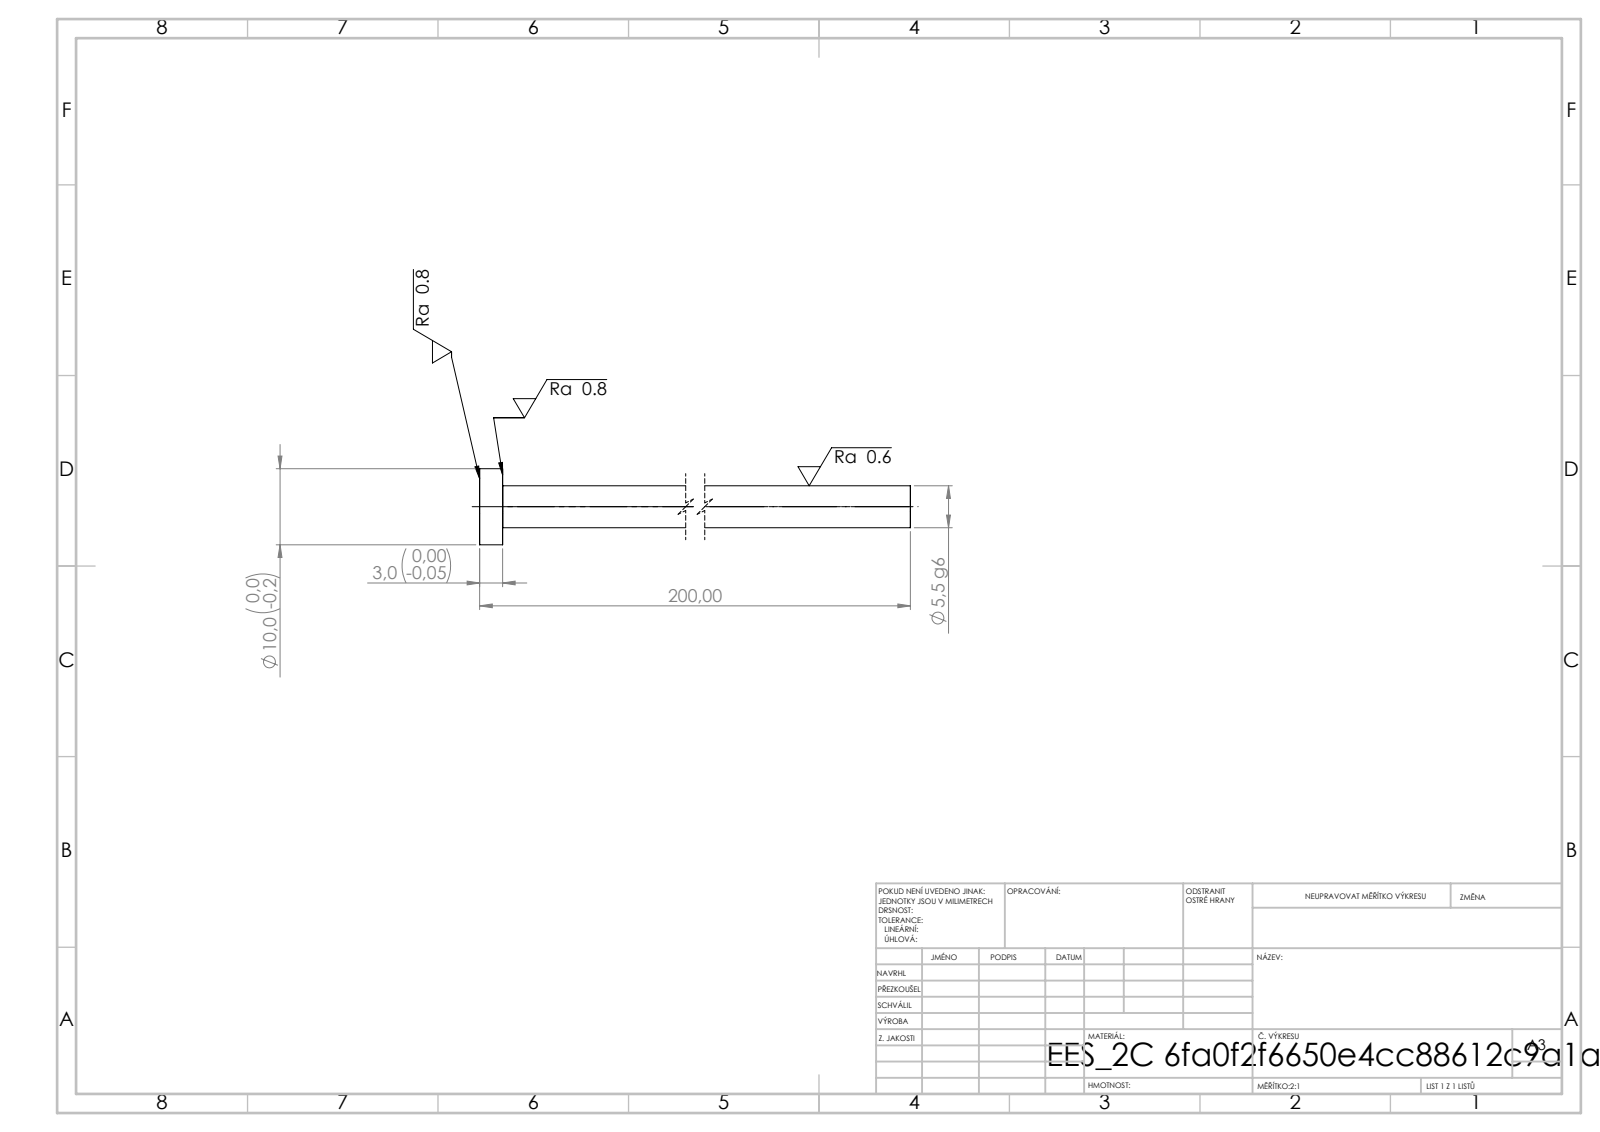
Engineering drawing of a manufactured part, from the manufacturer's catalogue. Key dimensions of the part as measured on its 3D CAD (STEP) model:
STEP written by: SolidWorks 2019 (CONFIG_CONTROL_DESIGN)
Units: millimetres
Bodies: 1 solid, 7 faces (3 planar, 4 cylindrical, 0 other)
Overall size (bounding box): 200 × 10 × 10
Volume: 4 916 mm³ · Surface area: 3 655 mm²
Round bosses / shafts (diameter × count): ⌀10 ×1, ⌀5.5 ×1
Main face-to-face distances: 3, 200, 197
